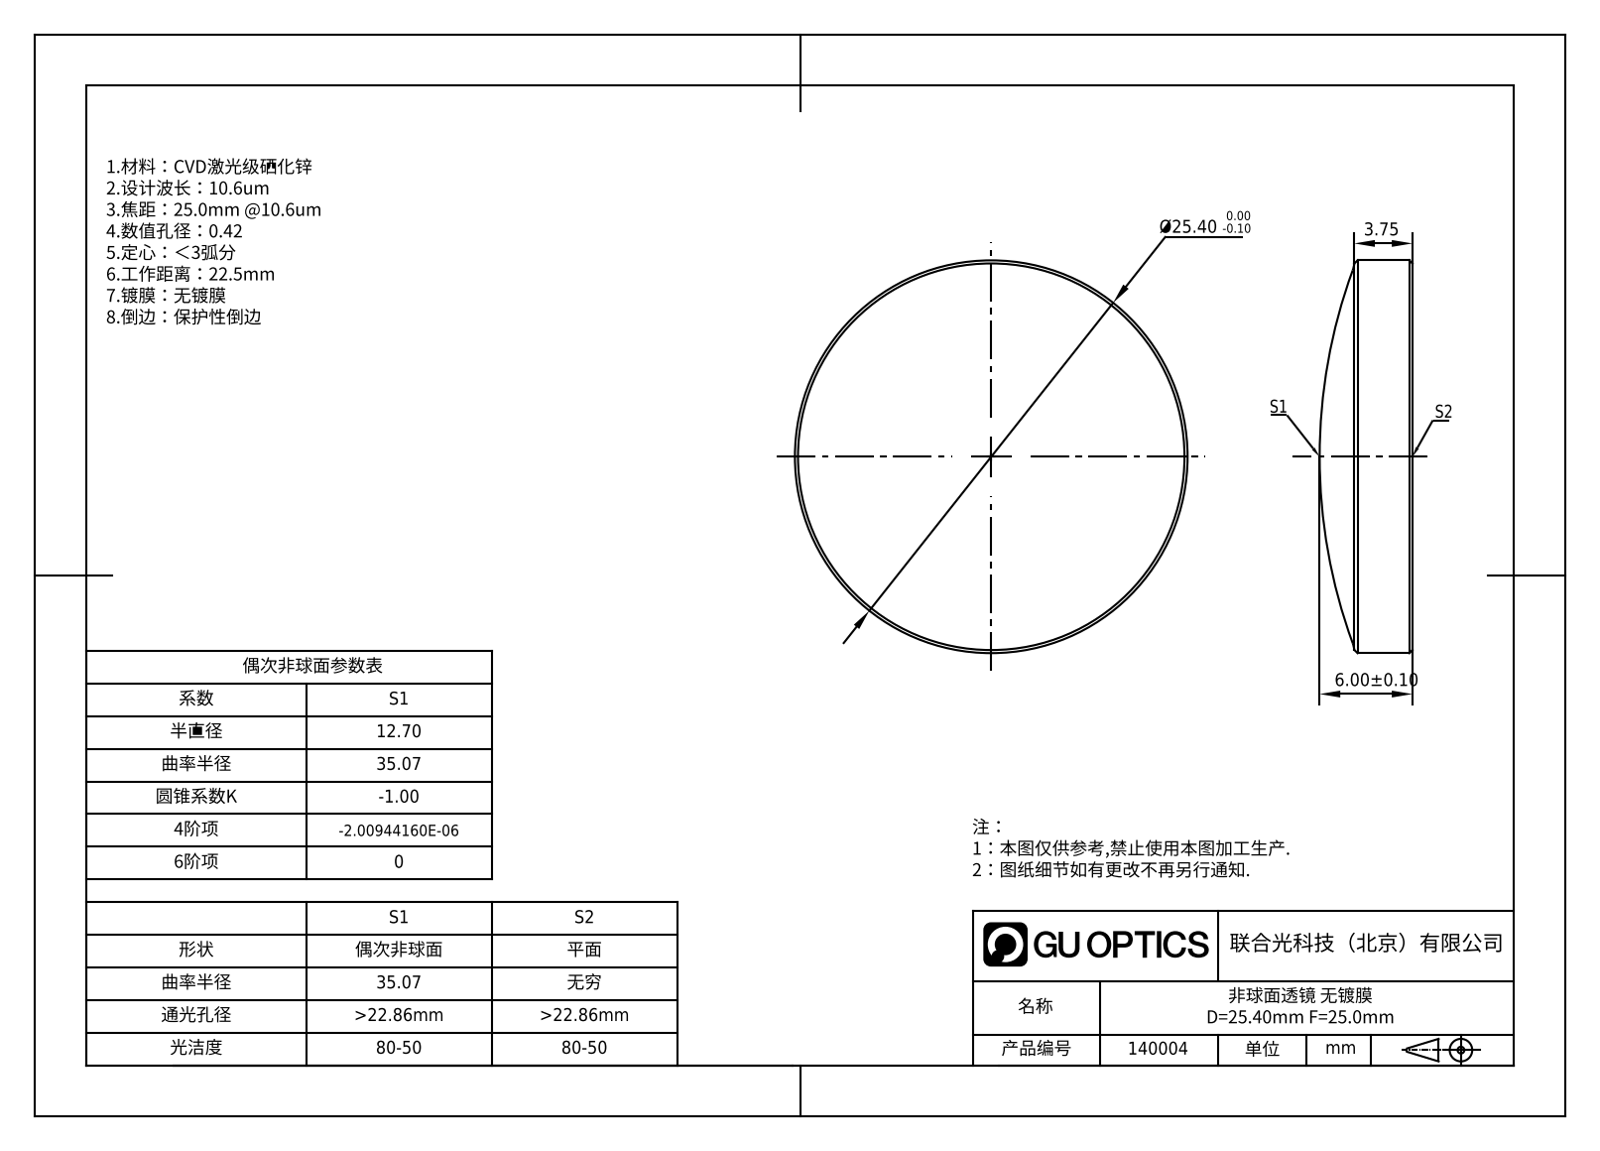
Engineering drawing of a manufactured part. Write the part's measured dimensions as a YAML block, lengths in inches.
part_name: "140004"
step_written_by: "SolidWorks 2020 (CONFIG_CONTROL_DESIGN)"
units: inches
bodies: {solids: 1, faces: 5, planar: 1, cylindrical: 2, other: 2}
overall_size: [1, 1, 0.236]
volume: 0.151
surface_area: 2.058
round_bosses_or_shafts:
  - {diameter: 1, count: 1}
